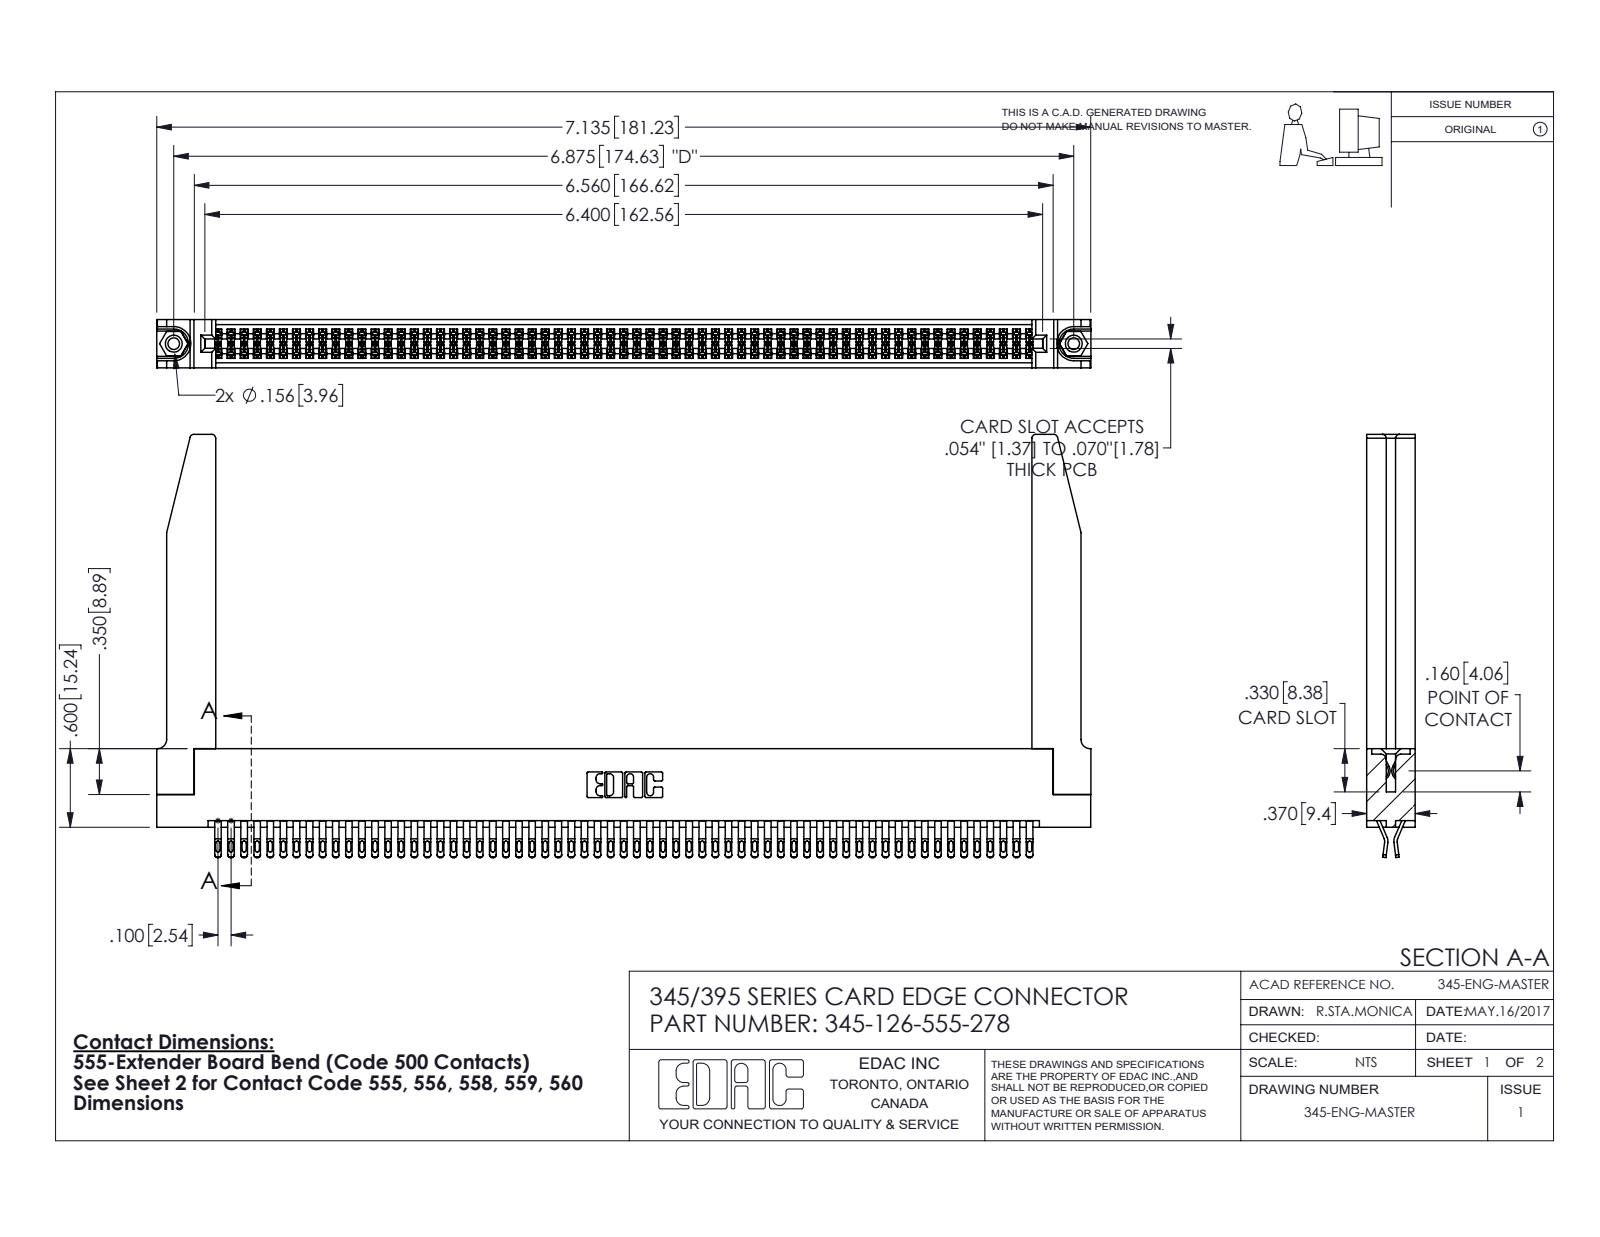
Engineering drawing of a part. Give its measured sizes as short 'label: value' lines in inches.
name: 345 Part_Flush Mounting Lugs - 0.156 Dia-TH; 345-250-001_345-250-001-102; 345-220-078_345-220-078; 345-126-555-278 (+1 more)
written by: SolidWorks 2016 (CONFIG_CONTROL_DESIGN)
unit: in
bodies: 131 solids, 7416 faces (4128 planar, 3236 cylindrical, 52 other)
size: 7.136 × 3.232 × 0.37
volume: 1.583 in³; area: 54.83 in²
holes: 2× ⌀0.089, 2× ⌀0.125, 2× ⌀0.156, 1× ⌀0.064
bosses: 2× ⌀0.155
rounds: 315× R0.016, 252× R0.02, 189× R0.006, 22× R0.01, 8× R0.03, 6× R0.007, 6× R0.031, 3× R0.026
face distances: 0.072, 0.298, 0.37, 0.025, 0.2, 0.098, 0.272, 0.225, 0.175, 0.148
hole spacings: 0.27, 6.639, 6.875
